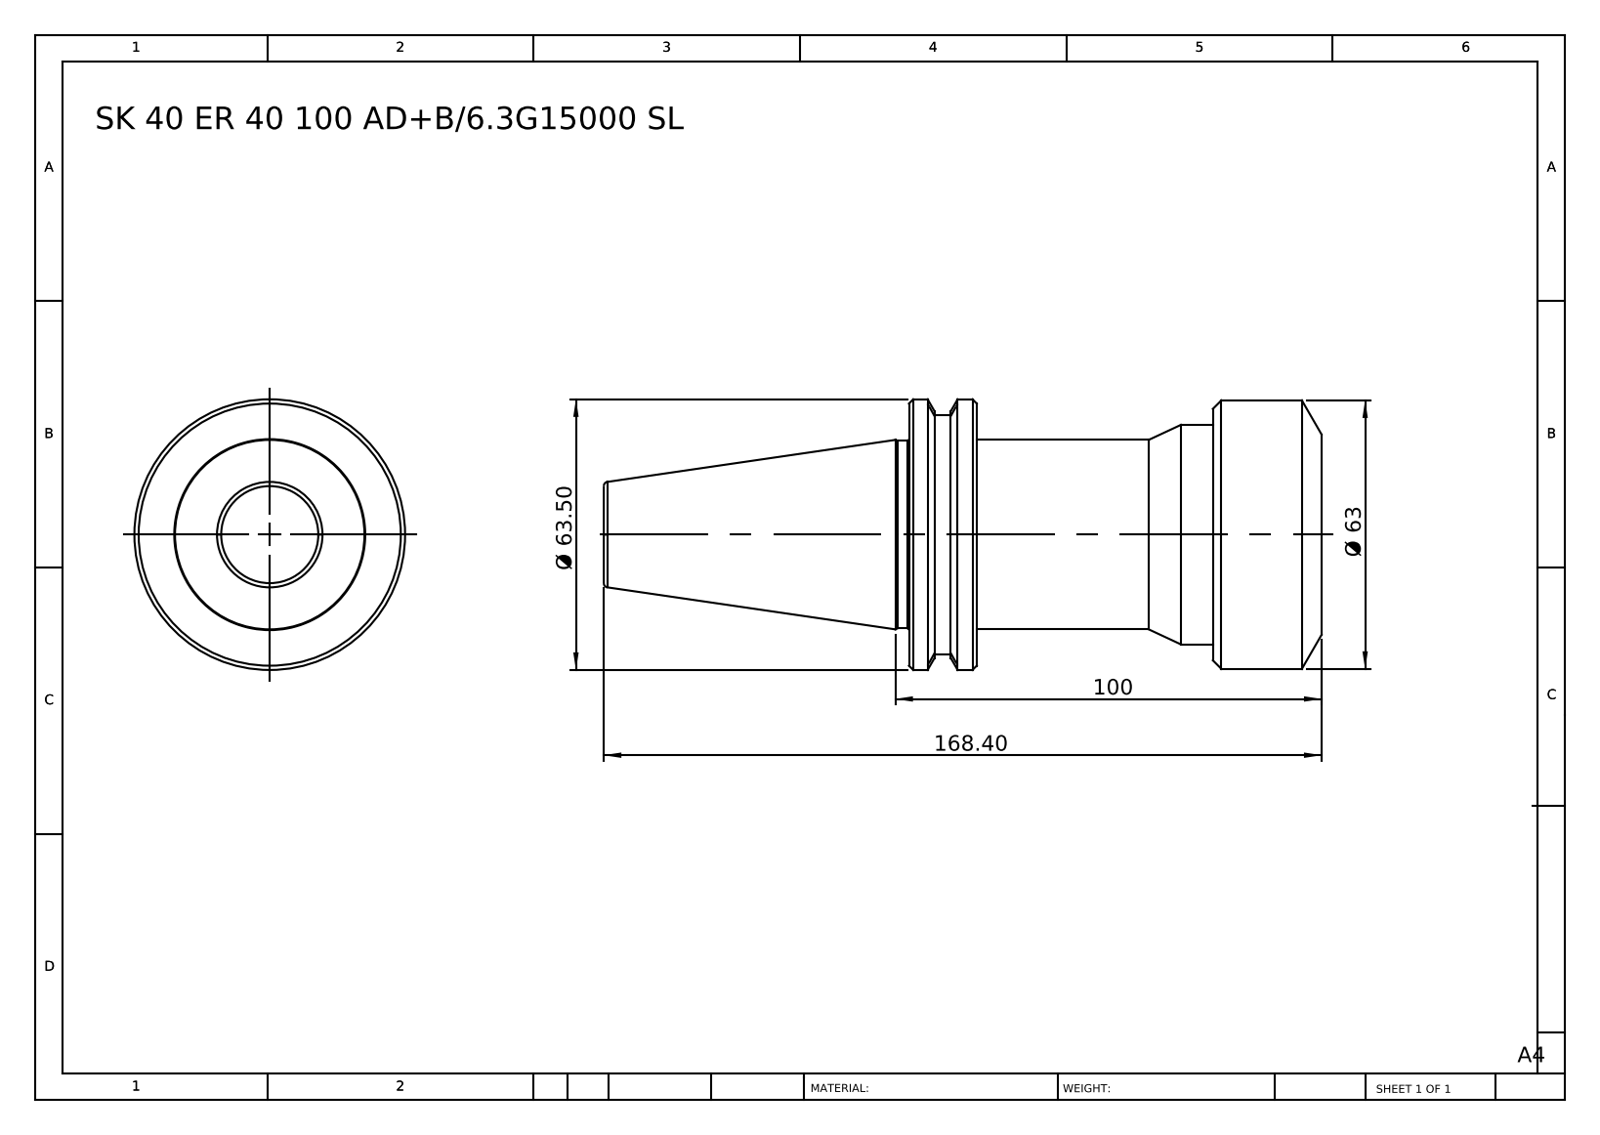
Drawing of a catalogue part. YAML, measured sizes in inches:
part_name: "SK 40 ER 40 100 AD-6.3G15000 SL"
step_written_by: "SolidWorks 2014 (CONFIG_CONTROL_DESIGN)"
units: inches
bodies: {solids: 1, faces: 53, planar: 7, cylindrical: 14, other: 32}
overall_size: [6.63, 2.5, 2.5]
volume: 17.39
surface_area: 49.23
round_bosses_or_shafts:
  - {diameter: 2.5, count: 1}
  - {diameter: 2.48, count: 1}
  - {diameter: 2.205, count: 1}
  - {diameter: 2.028, count: 1}
  - {diameter: 1.752, count: 1}
  - {diameter: 1.732, count: 1}
face_to_face_distances: [3.185, 3.811, 0.626, 1.004, 2.181, 2.807, 6.63, 5.626, 3.445, 2.819]
